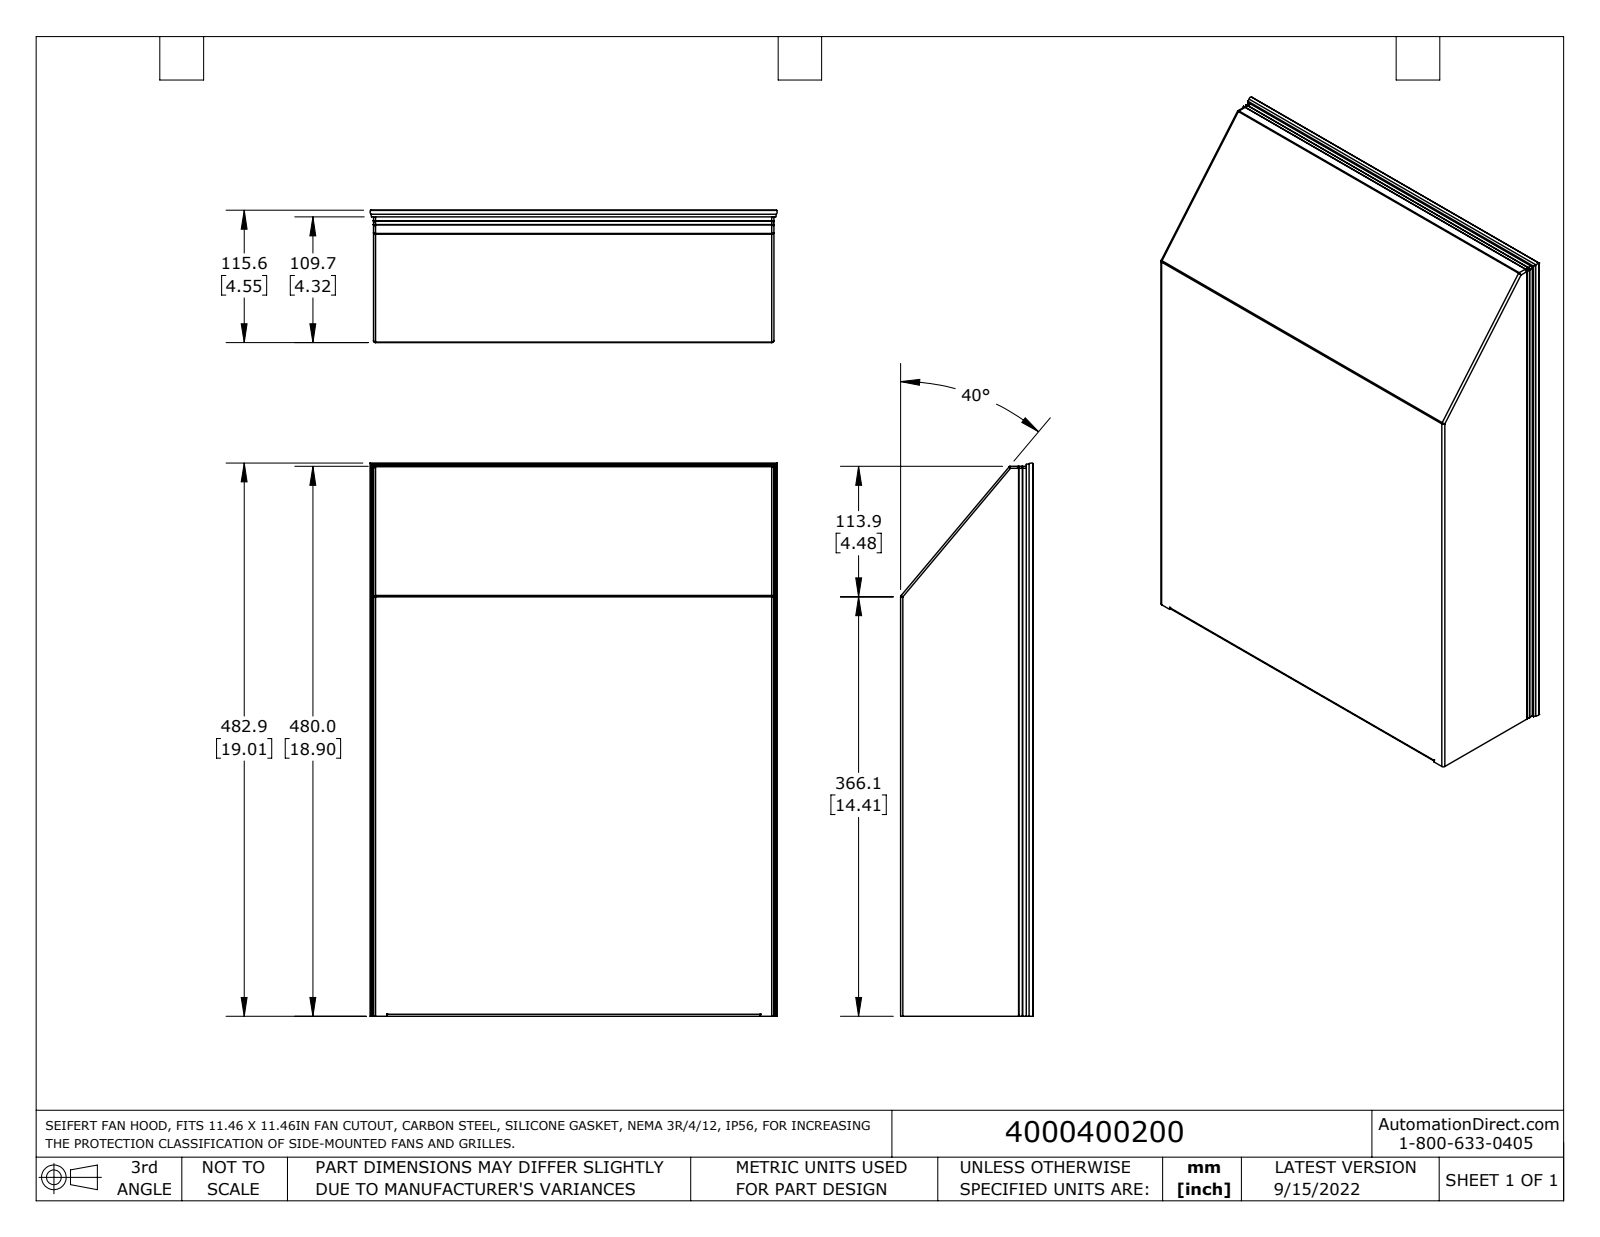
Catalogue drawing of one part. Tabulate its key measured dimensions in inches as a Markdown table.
| quantity | value |
| --- | --- |
| part name | 44999 |
| STEP written by | SolidWorks 2021 (AUTOMOTIVE_DESIGN) |
| units | inches |
| bodies | 4 solids, 304 faces (139 planar, 156 cylindrical, 9 other) |
| overall size | 19.012 × 13.992 × 4.549 |
| volume | 22.92 in³ |
| surface area | 1 128 in² |
| round holes (diameter × count) | 0.217 × 4 |
| partial cylindrical surfaces (radius × count) | 0.118 × 19, 0.004 × 12, 0.278 × 12, 1.181 × 12, 0.031 × 9, 0.071 × 8, 0.008 × 6, 0.039 × 6 |
| main face-to-face distances | 0.031, 13.732, 13.701, 13.764, 0.059, 13.386, 0.378, 0.346, 13.354, 0.319 |
| hole center spacings | 11.28, 14.567, 18.424 |
